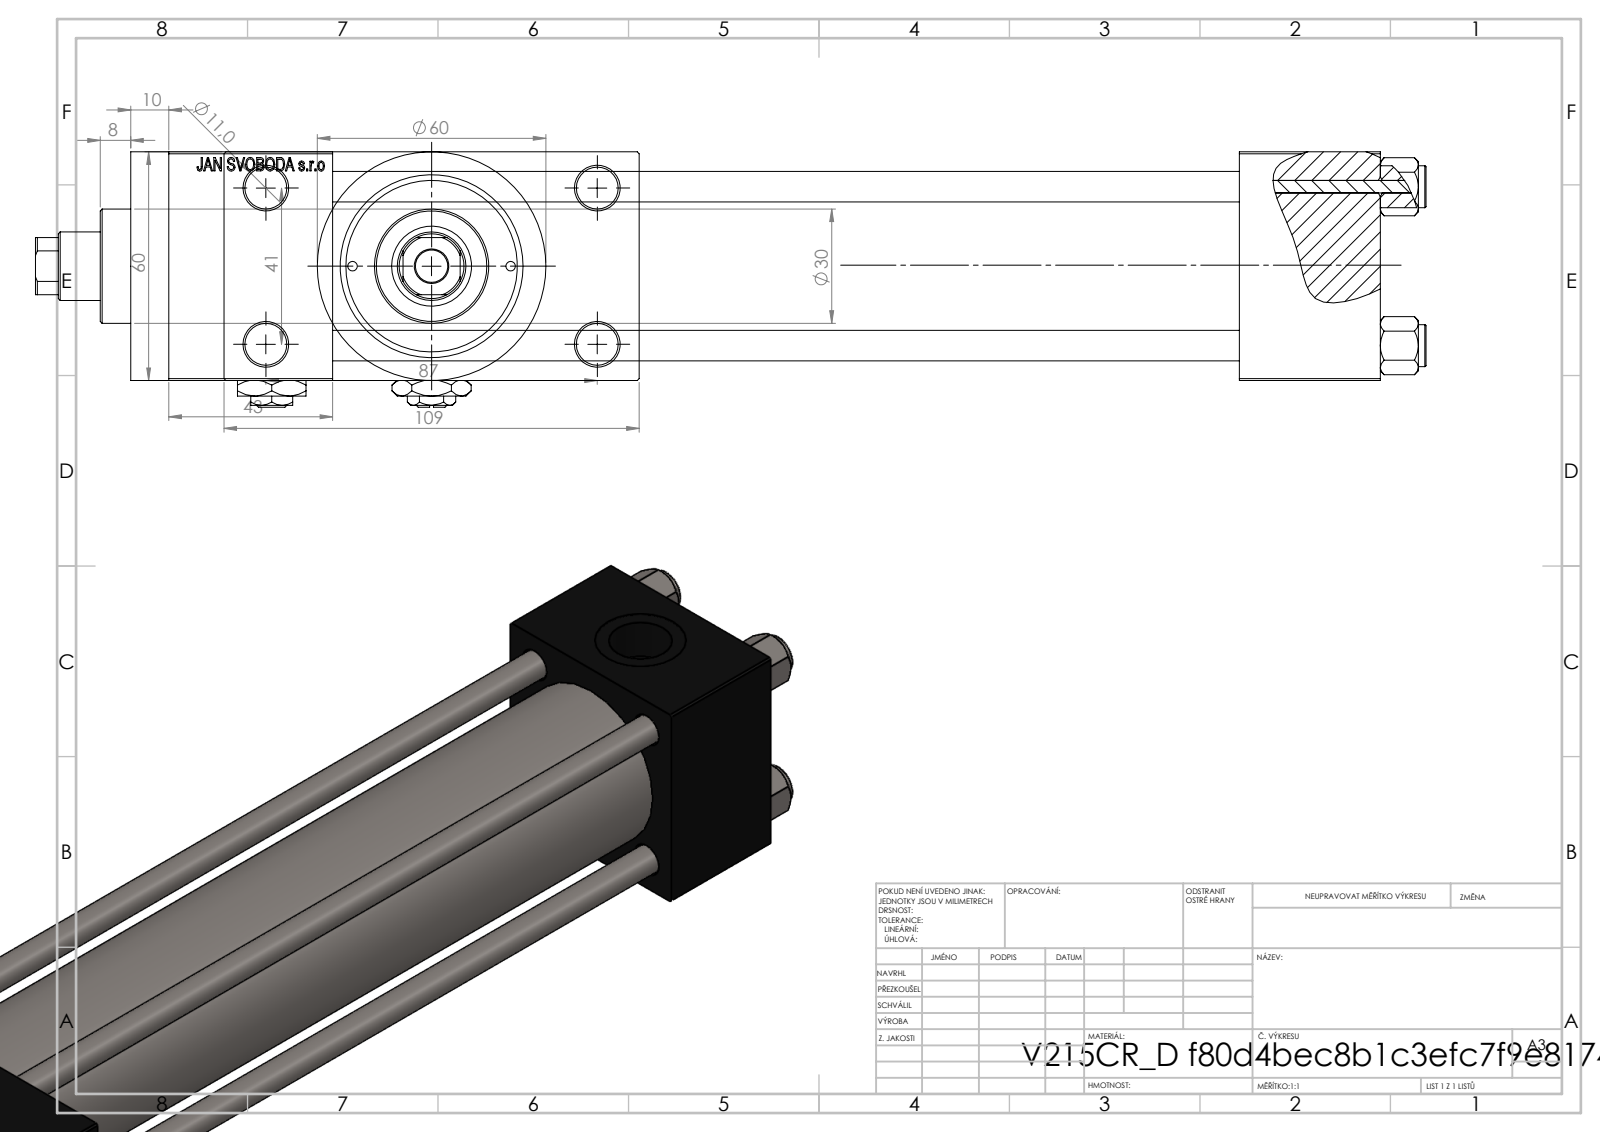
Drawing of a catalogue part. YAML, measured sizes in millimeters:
part_name: "V215CR_D_Body; V215_VC_A; V215CR_VCP_D; V215CR_D_TYCINKA (+2 more)"
step_written_by: "SolidWorks 2019 (CONFIG_CONTROL_DESIGN)"
units: millimeters
bodies: {solids: 12, faces: 1161, planar: 524, cylindrical: 97, other: 540}
overall_size: [365, 109, 67]
volume: 672064
surface_area: 199042
round_holes:
  - {diameter: 8, count: 4}
  - {diameter: 11, count: 4}
  - {diameter: 2.5, count: 2}
  - {diameter: 7, count: 2}
  - {diameter: 16.66, count: 2}
  - {diameter: 24, count: 2}
  - {diameter: 8.5, count: 1}
  - {diameter: 18, count: 1}
  - {diameter: 21, count: 1}
  - {diameter: 31, count: 1}
  - {diameter: 40, count: 1}
  - {diameter: 45, count: 1}
round_bosses_or_shafts:
  - {diameter: 11, count: 4}
  - {diameter: 60, count: 1}
  - {diameter: 46, count: 1}
  - {diameter: 30, count: 1}
partial_cylinders:
  - {radius: 8.5, count: 1}
face_to_face_distances: [60, 24.5, 84.5, 238, 37, 275, 43, 318, 281, 109]
hole_center_spacings: [20.85, 22.65, 29.49, 30.62, 41.7, 46.53, 47.15, 48.09]
